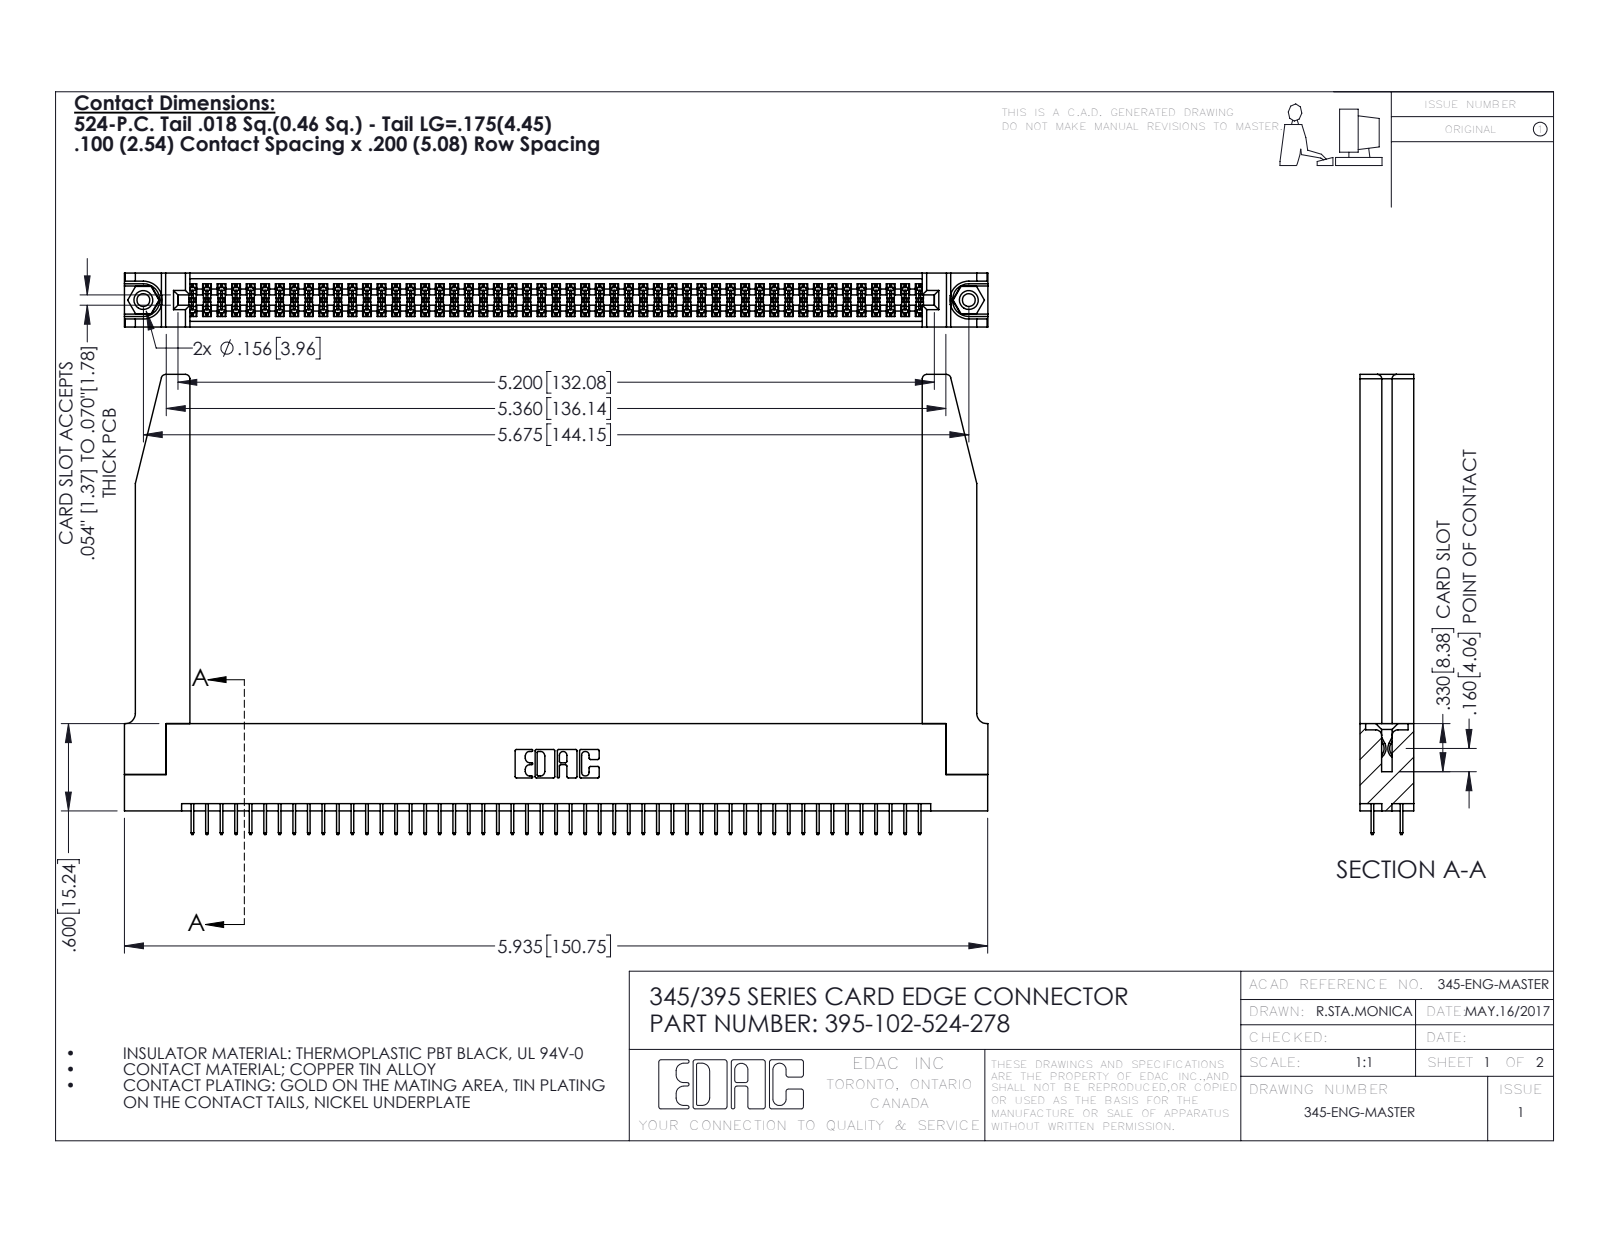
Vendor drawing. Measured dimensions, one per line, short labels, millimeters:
name: 345 Part_Flush Mounting Lugs - 0.156 Dia-TH; 345-250-001_345-250-001-102; 395-102-524-278; 345-220-078_345-220-078 (+1 more)
written by: SolidWorks 2016 (CONFIG_CONTROL_DESIGN)
unit: mm
bodies: 107 solids, 5868 faces (4200 planar, 1616 cylindrical, 52 other)
size: 150.8 × 80.3 × 9.4
volume: 22 350 mm³; area: 28 150 mm²
holes: 2× ⌀2.3, 2× ⌀3.2, 2× ⌀4, 1× ⌀1.6
bosses: 2× ⌀3.9
rounds: 153× R0.2, 22× R0.3, 8× R0.8, 6× R0.2, 6× R0.8, 3× R0.7, 2× R0.4, 2× R0.5
face distances: 1.8, 9.4, 7.6, 5.1, 2.5, 6.9, 0.6, 5.7, 1.8, 3.8
hole spacings: 6.9, 138.2, 144.1
